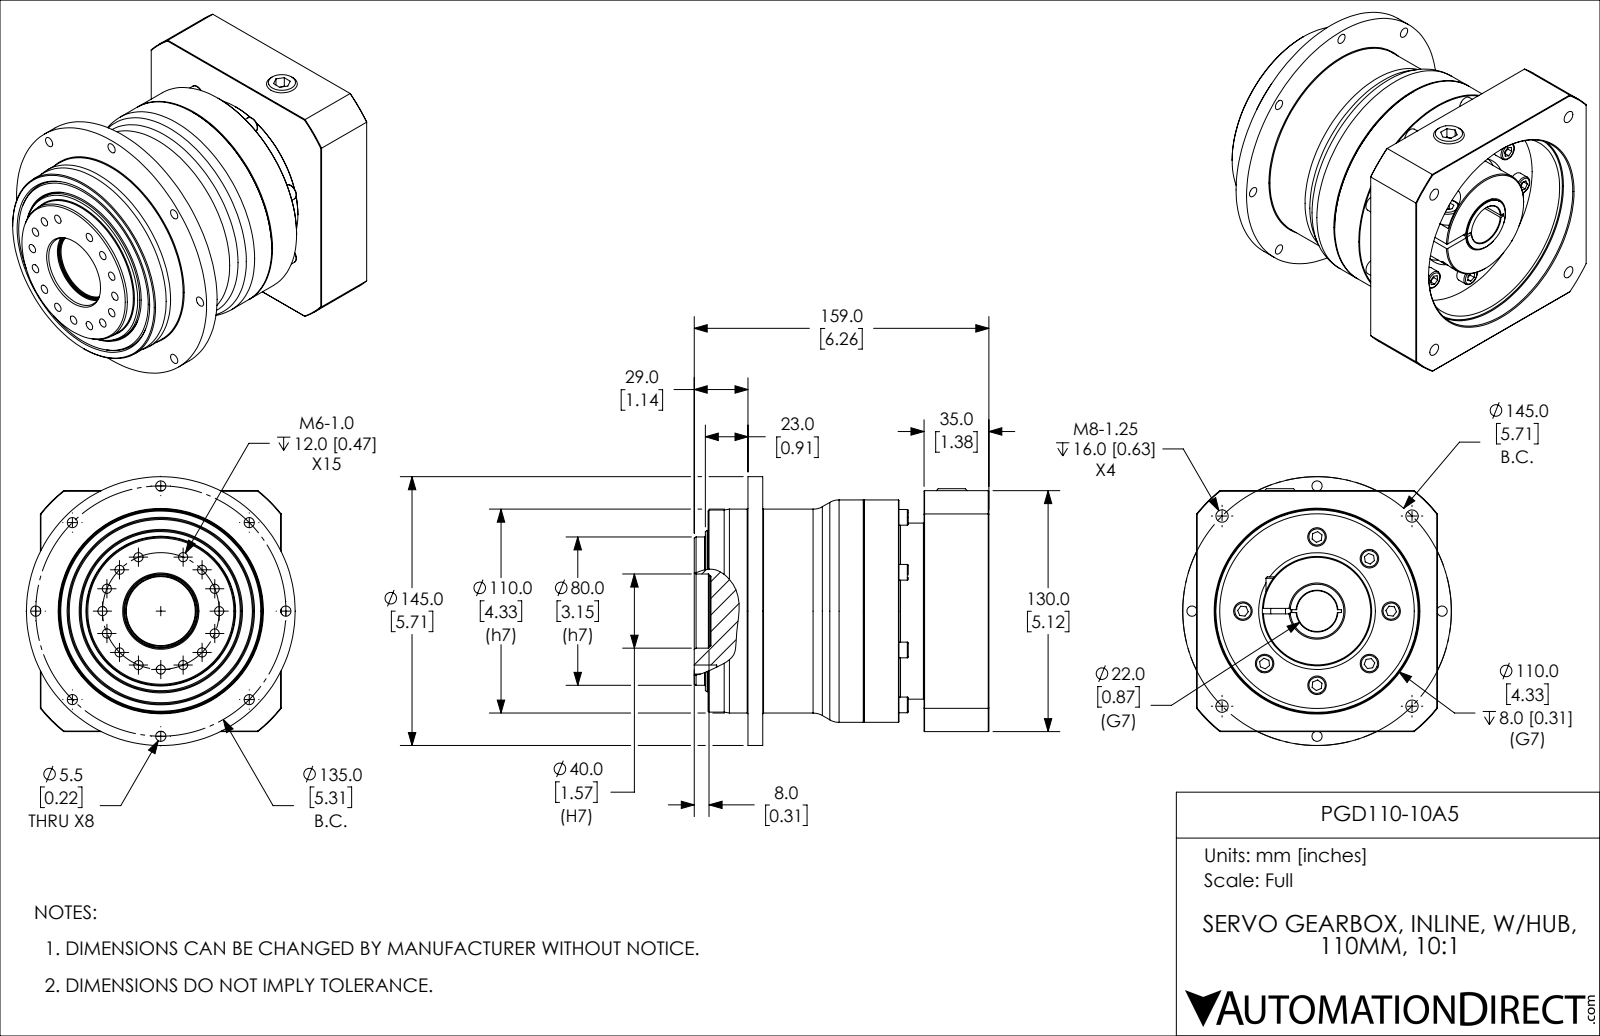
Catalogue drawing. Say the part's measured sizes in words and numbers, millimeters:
The part is named "PGD110-10A5". Its 3-D file was written by "SolidWorks 2015 (AUTOMOTIVE_DESIGN)". It is 11 solids with 582 faces: 302 planar, 197 cylindrical and 83 other. Overall it measures 159.02 by 145 by 145 millimeters. Its volume is 1 513 000 cubic millimeters and its surface area 159 834 square millimeters. Round holes: 11 of diameter 4.92, 8 of diameter 5.5, 4 of diameter 4.92, 3 of diameter 6.65, 2 of diameter 8, 1 of diameter 6.65, 1 of diameter 8.8, 1 of diameter 13, 1 of diameter 15, 1 of diameter 28, 1 of diameter 37.2, 1 of diameter 39.2. Round bosses or shafts: 7 of diameter 10, 1 of diameter 145, 1 of diameter 120, 1 of diameter 111, 1 of diameter 110, 1 of diameter 95, 1 of diameter 80, 1 of diameter 54.5. Partial cylindrical surfaces (rounded edges, fillets, slot ends): 7 of radius 4.25, 1 of radius 7, 1 of radius 83.2. The main face-to-face distances are 4, 117.02, 22.02, 129.4, 6, 95, 91, 26.02, 35, 126. The hole center spacings are 40.25, 62.62, 84.71, 97.35, 12.29, 52.38, 74.49, 44.54.
